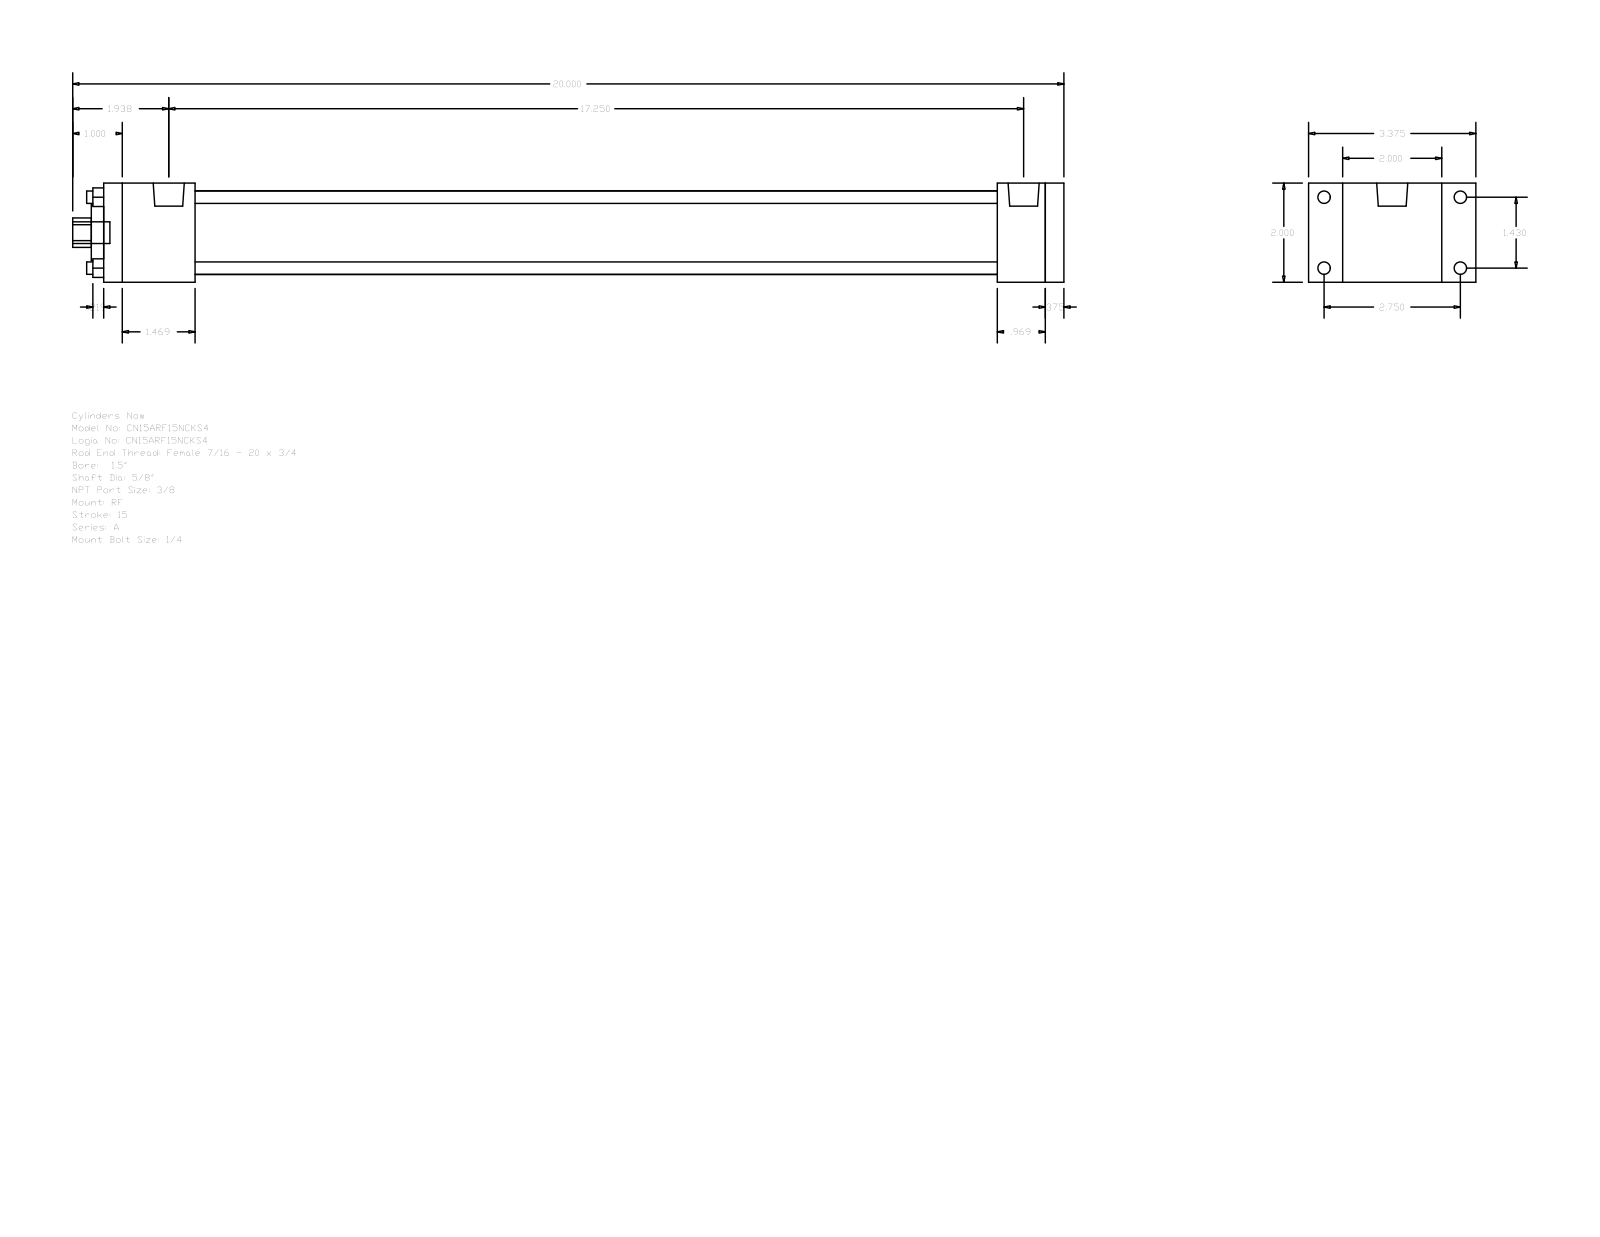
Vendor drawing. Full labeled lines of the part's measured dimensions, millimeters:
Part name (STEP PRODUCT): A_RF__0150_0.625
STEP written by: GSSL Pune (CONFIG_CONTROL_DESIGN)
Units: millimetres
Bodies: 0 solids, 92 faces (64 planar, 28 cylindrical, 0 other)
Overall size (bounding box): 508 × 85.72 × 50.8
Round holes (diameter × count): ⌀6.35 ×4, ⌀15.88 ×1, ⌀28.57 ×1, ⌀42.93 ×1
Round bosses / shafts (diameter × count): ⌀6.35 ×4, ⌀5.56 ×4, ⌀15.93 ×2, ⌀11.11 ×1
Partial cylindrical surfaces — rounded edges, fillets, slot ends (radius × count): R7.54 ×1
Main face-to-face distances: 50.8, 9.52, 482.6, 492.12, 457.99, 24.61, 34.13, 46.83, 411.16, 435.77
Hole centre spacings: 25.68, 36.32, 51.36
